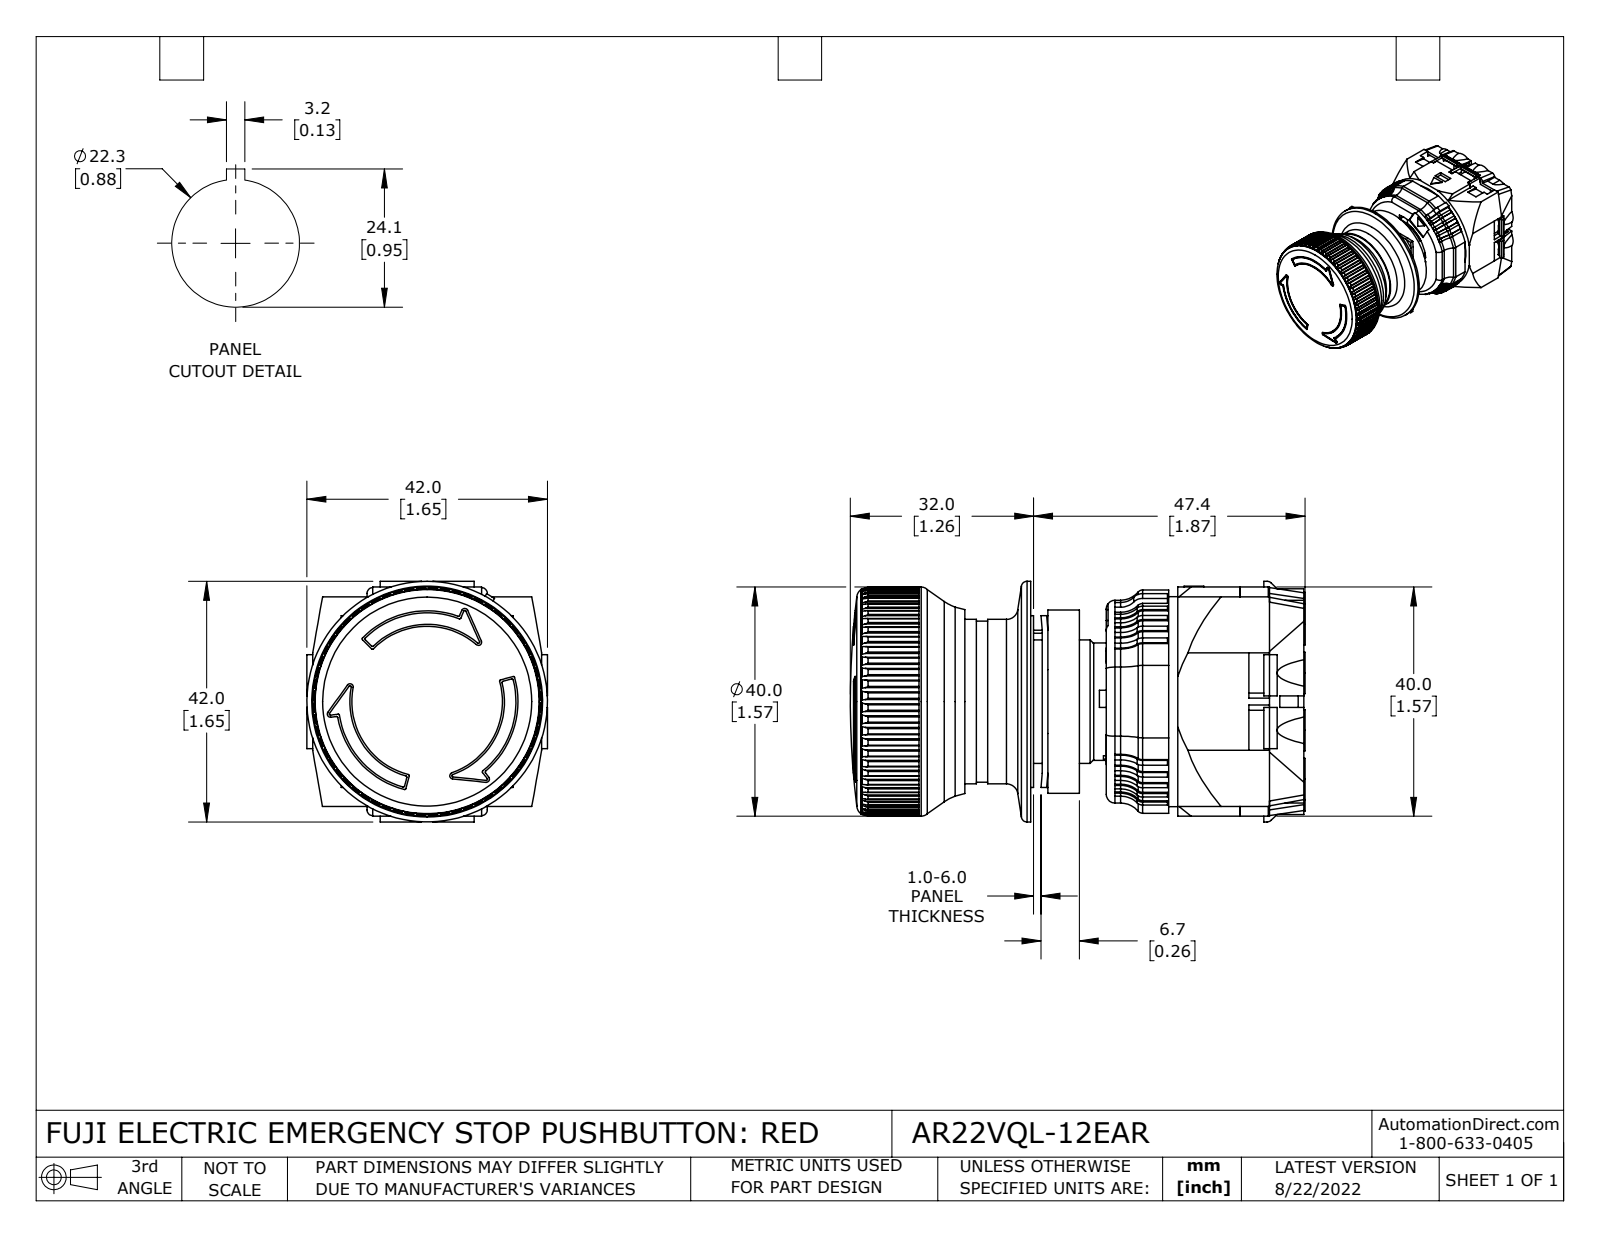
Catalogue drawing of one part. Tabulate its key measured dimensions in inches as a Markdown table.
| quantity | value |
| --- | --- |
| part name | AR22VQL-12EAR |
| STEP written by | SolidWorks 2021 (CONFIG_CONTROL_DESIGN) |
| units | inches |
| bodies | 8 solids, 1459 faces (645 planar, 600 cylindrical, 214 other) |
| overall size | 3.126 × 1.654 × 1.654 |
| volume | 3.81 in³ |
| surface area | 53.8 in² |
| round holes (diameter × count) | 0.138 × 12, 0.244 × 12, 0.315 × 1, 0.689 × 1, 0.827 × 1, 0.839 × 1, 0.866 × 1, 0.878 × 1, 1.102 × 1, 1.169 × 1, 1.443 × 1 |
| round bosses / shafts (diameter × count) | 0.283 × 12, 1.654 × 1, 1.575 × 1, 1.26 × 1, 1.181 × 1, 1.13 × 1, 1.106 × 1, 0.882 × 1 |
| partial cylindrical surfaces (radius × count) | 0.008 × 146, 0.016 × 64, 0.049 × 19, 0.148 × 19, 0.165 × 12, 0.039 × 10, 0.022 × 6, 0.059 × 4 |
| main face-to-face distances | 0.039, 0.728, 0.453, 0.394, 1.76, 0.709, 0.827, 0.118, 0.929, 0.157 |
| hole center spacings | 0.641, 0.907, 0.325, 0.349, 0.394, 0.585, 0.713, 0.735 |
